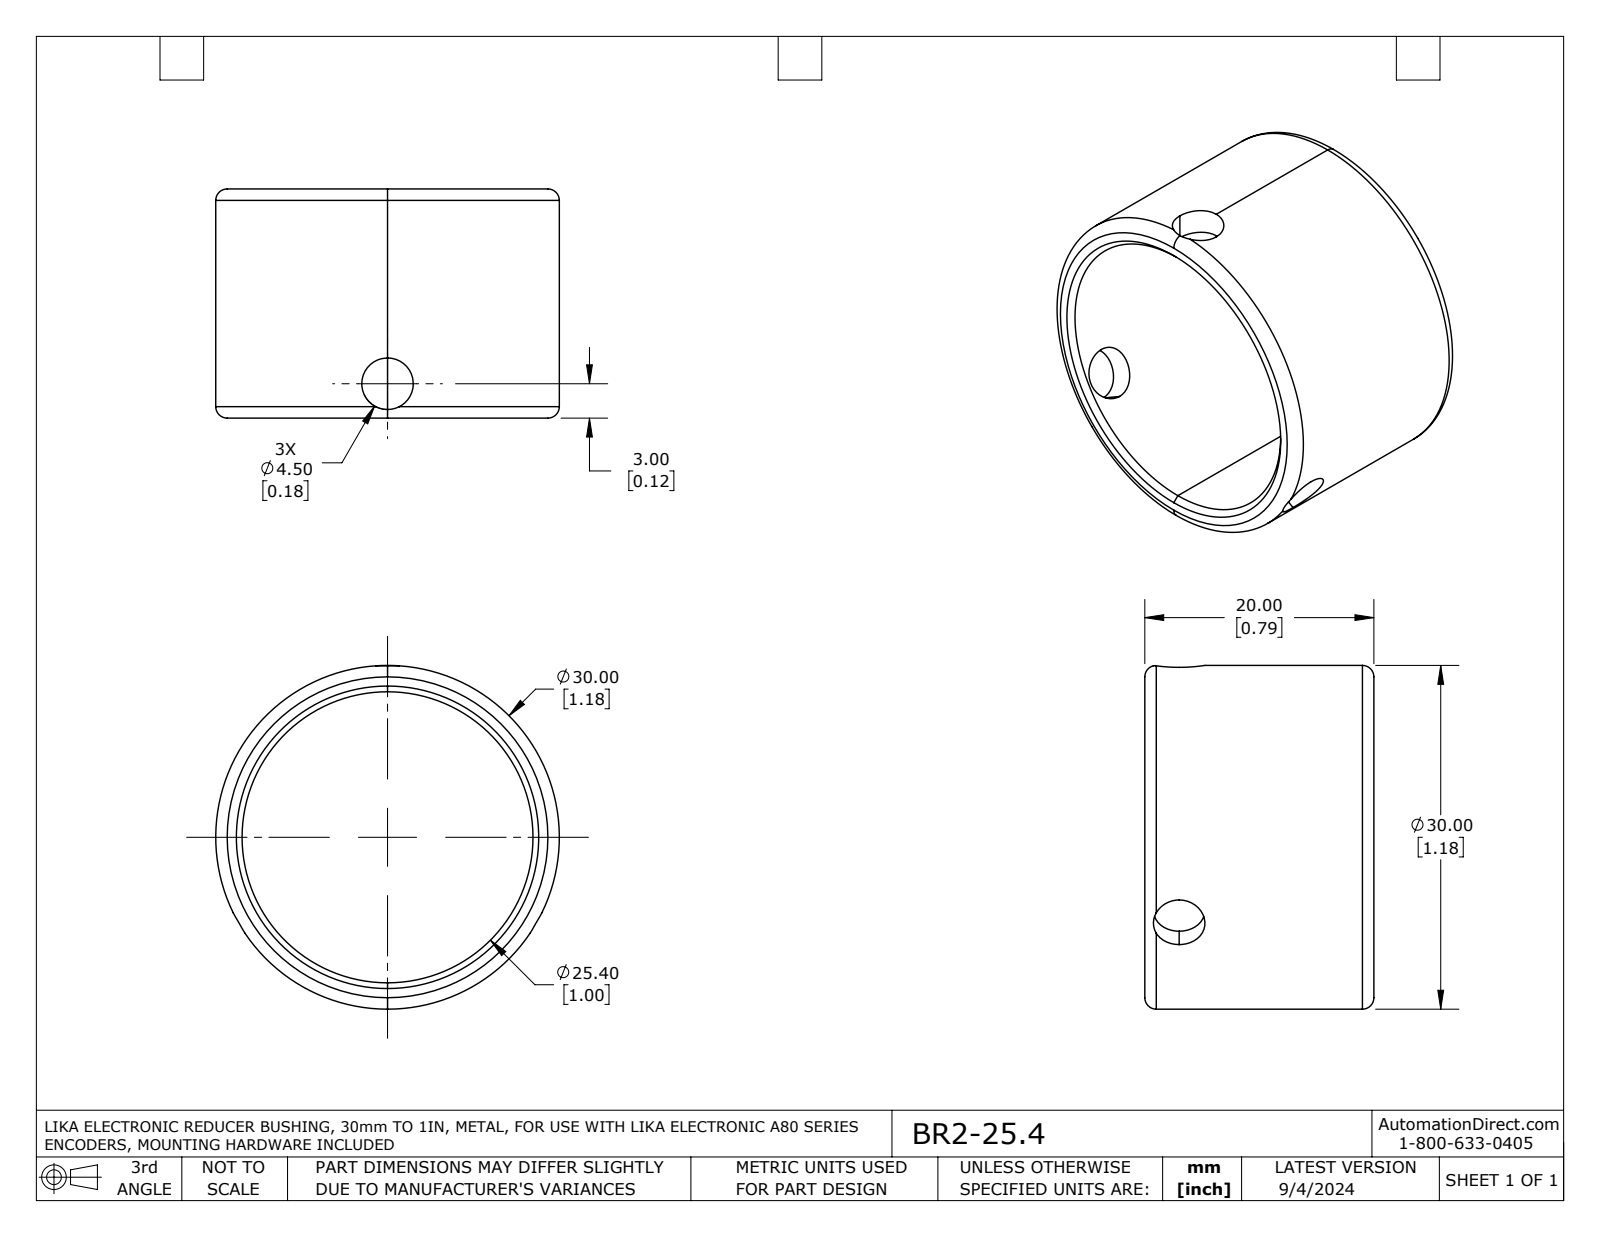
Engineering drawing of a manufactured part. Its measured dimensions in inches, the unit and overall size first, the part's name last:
Units: inches
Overall size (bounding box): 1.181 × 1.181 × 0.787
Round holes (diameter × count): ⌀0.177 ×3, ⌀1 ×1
Round bosses / shafts (diameter × count): ⌀1.181 ×1
Main face-to-face distances: 0.787
Volume: 0.234 in³ · Surface area: 5.821 in²
Bodies: 1 solid, 25 faces (2 planar, 13 cylindrical, 10 other)
Part name (STEP PRODUCT): BR2-25.4
STEP written by: SolidWorks 2021 (AUTOMOTIVE_DESIGN)
